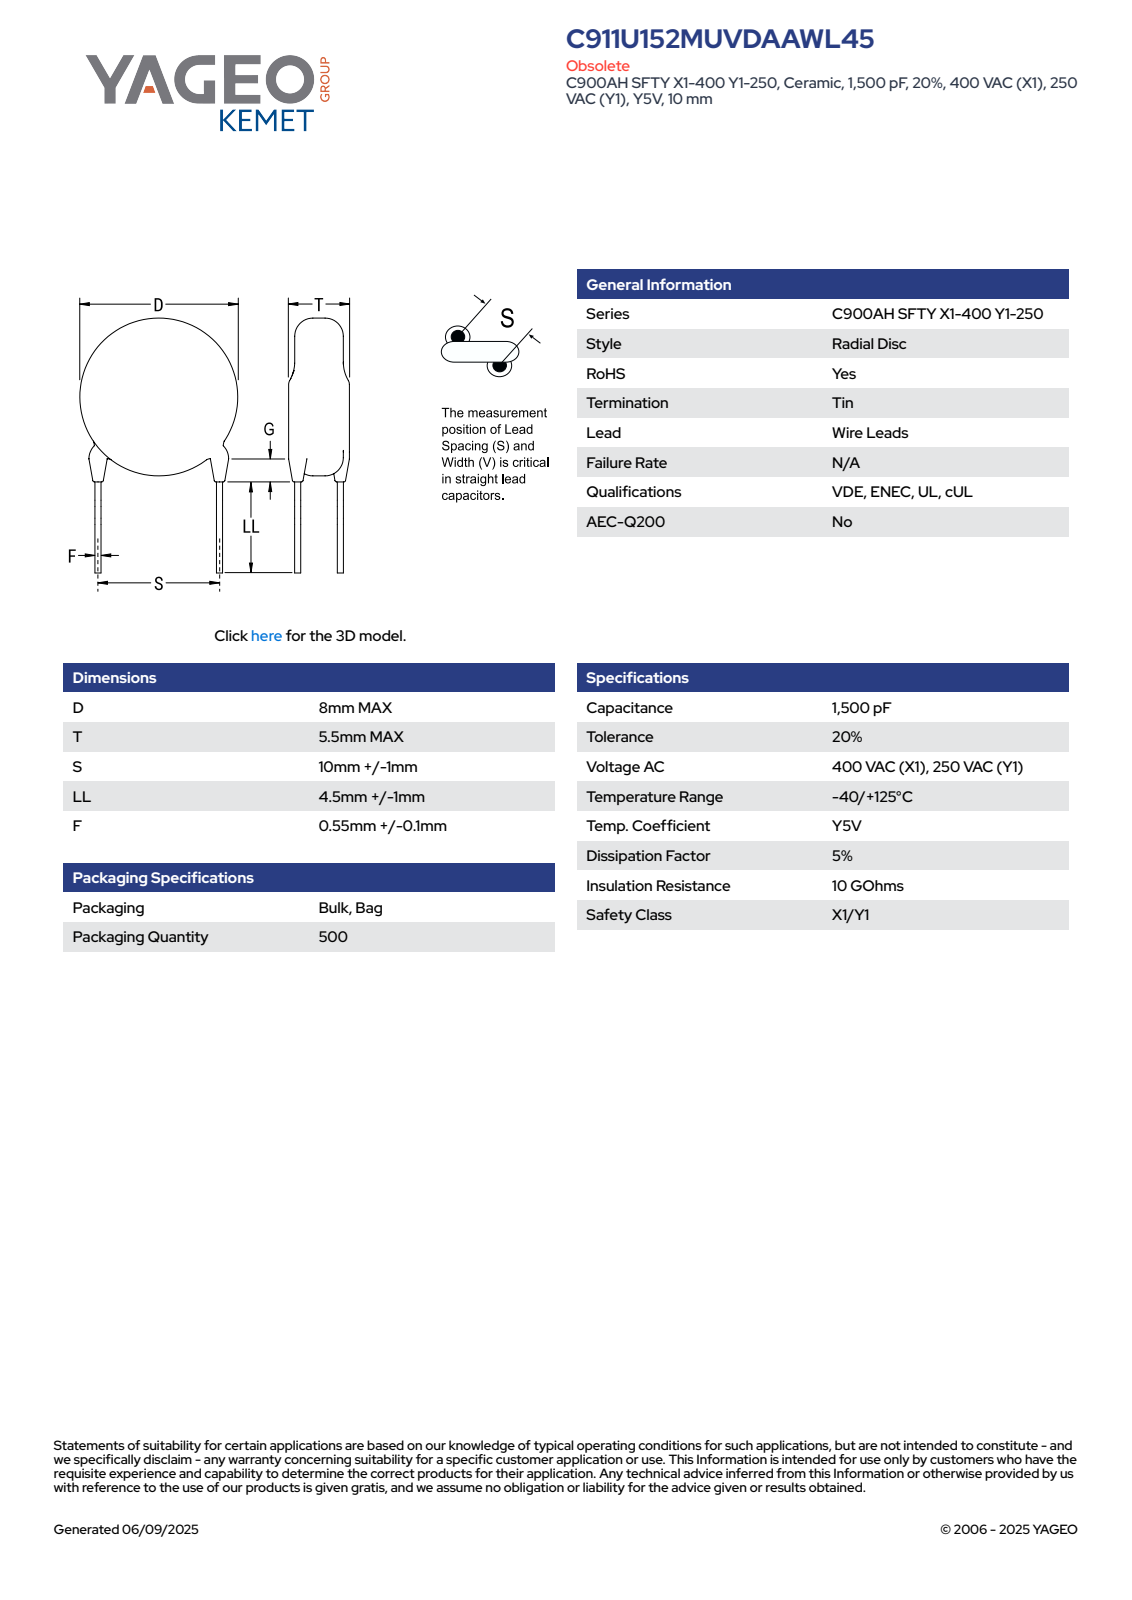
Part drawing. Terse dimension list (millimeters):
name: CCD_STC900_D8T5.5S10LL5.5F0.65G3
written by: SolidWorks 2014 (AUTOMOTIVE_DESIGN)
unit: mm
bodies: 4 solids, 83 faces (61 planar, 6 cylindrical, 16 other)
size: 13.91 × 9.99 × 5.5
volume: 275 mm³; area: 259 mm²
bosses: 2× ⌀0.65, 1× ⌀8
face distances: 5.5, 10.37, 9.45, 0.92, 0.4, 1.04, 3.77, 0.57, 2.73, 2.84
